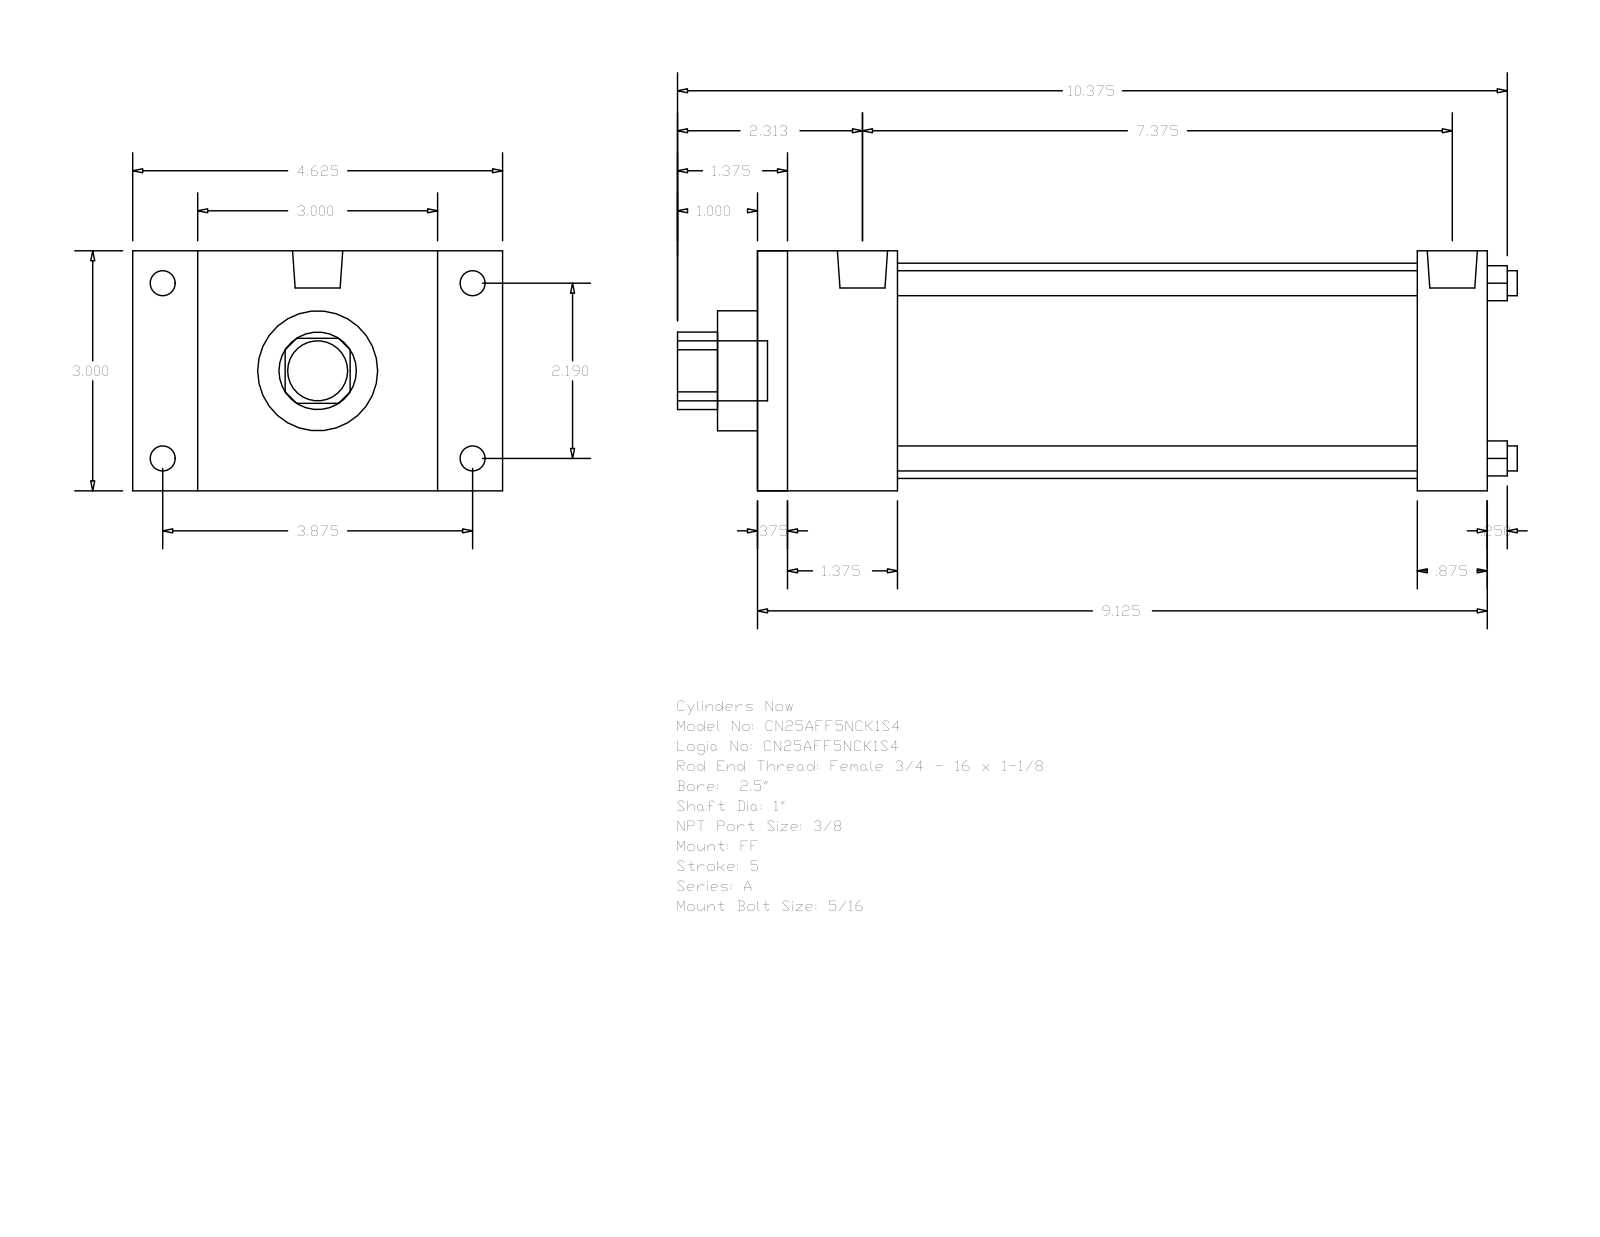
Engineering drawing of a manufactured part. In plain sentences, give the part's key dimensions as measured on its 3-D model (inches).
The part is named "A_FF__0250_1". Its 3-D file was written by "GSSL Pune (CONFIG_CONTROL_DESIGN)". It is 0 solids with 92 faces: 64 planar, 28 cylindrical and 0 other. Overall it measures 10.5 by 4.625 by 3 inches. Round holes: 4 of diameter 0.313, 1 of diameter 1, 1 of diameter 1.5, 1 of diameter 2.69. Round bosses or shafts: 4 of diameter 0.313, 4 of diameter 0.219, 2 of diameter 0.627, 1 of diameter 0.75. Partial cylindrical surfaces (rounded edges, fillets, slot ends): 1 of radius 0.484. The main face-to-face distances are 3, 9.125, 0.375, 8.75, 1.75, 8.25, 1.375, 7.875, 6.5, 7.375. The hole center spacings are 1.548, 2.19, 3.097.
